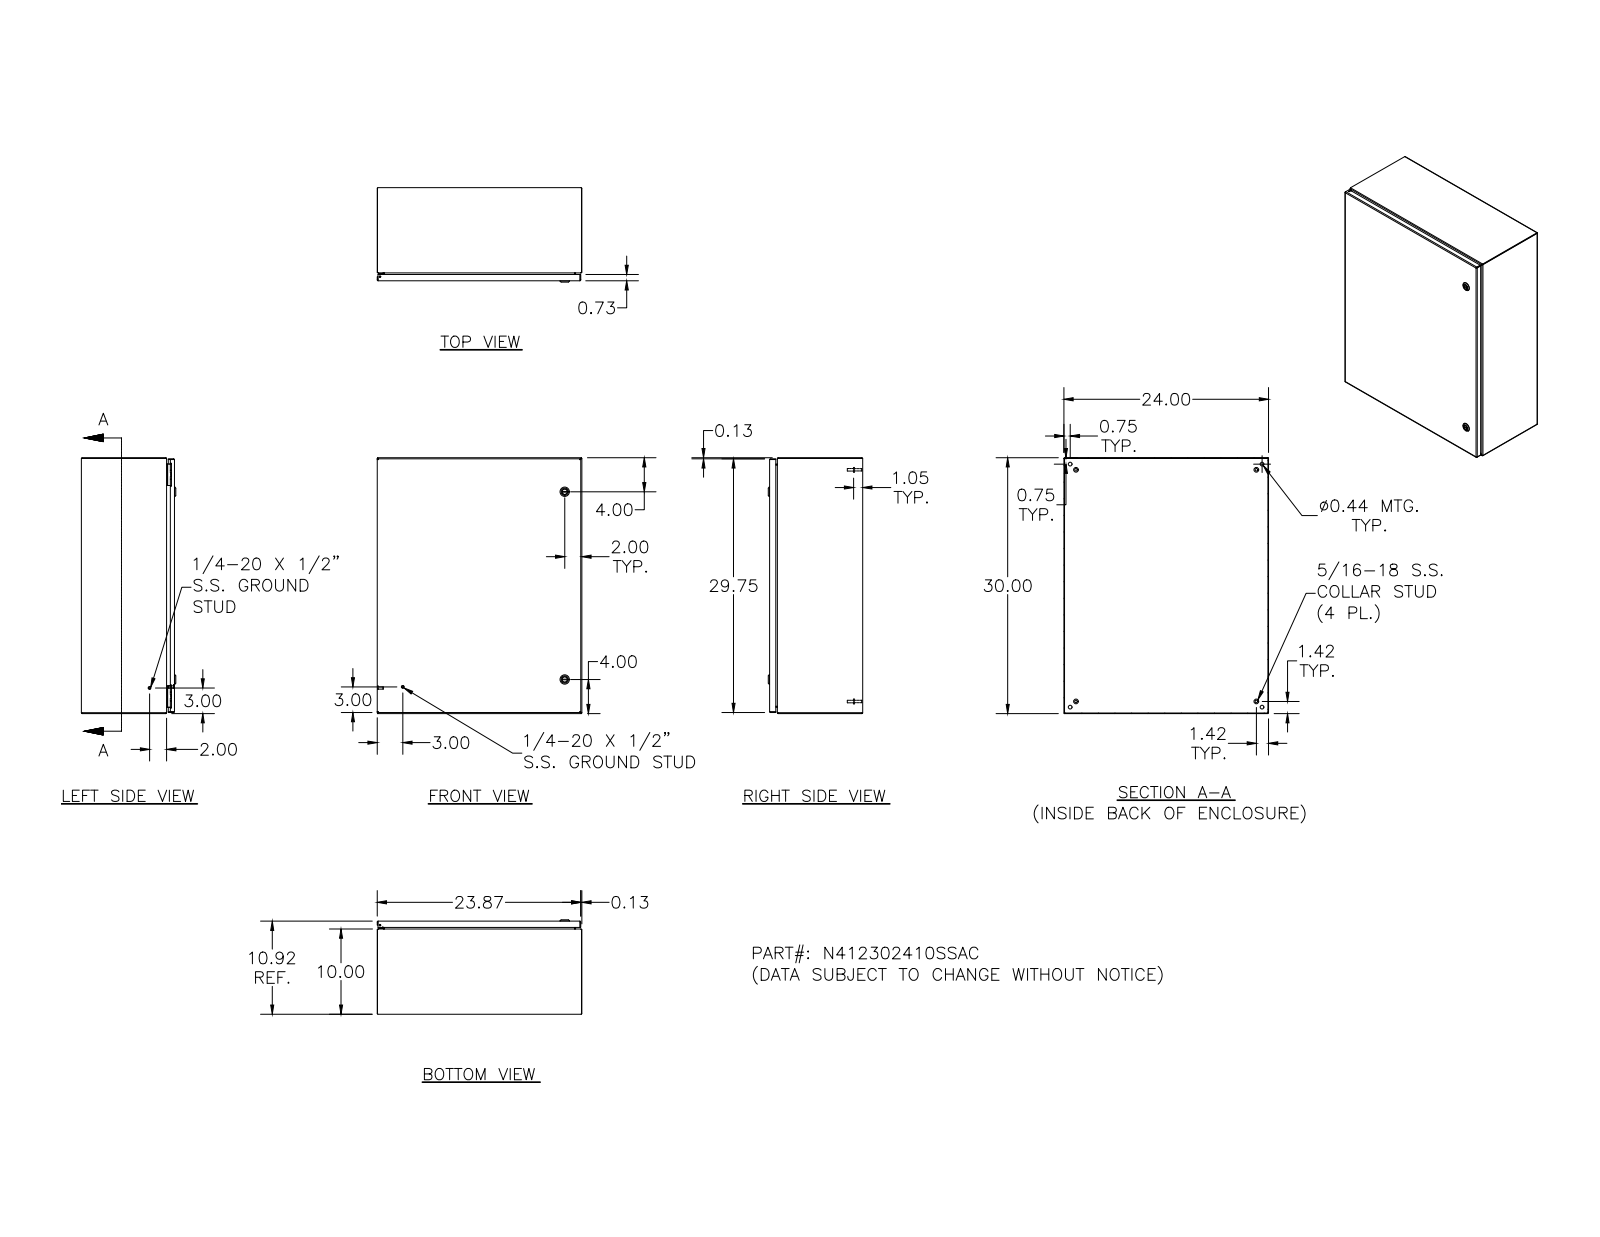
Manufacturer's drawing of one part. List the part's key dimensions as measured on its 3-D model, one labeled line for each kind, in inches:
Part name (STEP PRODUCT): N412302410SSAC; N412302410SSACBKP; 388151; N4123024SSACLID (+8 more)
STEP written by: Autodesk Inventor 2011 (AUTOMOTIVE_DESIGN)
Units: inches
Bodies: 42 solids, 1662 faces (698 planar, 588 cylindrical, 376 other)
Overall size (bounding box): 30 × 24 × 11.075
Volume: 203 in³ · Surface area: 5 506 in²
Round holes (diameter × count): ⌀0.188 ×5, ⌀0.093 ×4, ⌀0.152 ×4, ⌀0.167 ×4, ⌀0.172 ×4, ⌀0.437 ×4, ⌀0.156 ×2, ⌀0.197 ×2, ⌀0.315 ×2, ⌀0.394 ×2, ⌀0.402 ×2, ⌀0.634 ×2
Round bosses / shafts (diameter × count): ⌀0.25 ×10, ⌀0.563 ×4, ⌀0.36 ×4, ⌀0.32 ×4, ⌀0.3 ×4, ⌀0.275 ×4, ⌀0.256 ×4, ⌀0.164 ×4
Partial cylindrical surfaces — rounded edges, fillets, slot ends (radius × count): R0.05 ×26, R0.016 ×18, R0.016 ×16, R0.09 ×16, R0.02 ×15, R0.031 ×14, R0.125 ×14, R0.032 ×8
Main face-to-face distances: 0.074, 10.843, 10.917, 10.769, 23.926, 29.926, 23.852, 24, 30, 29.852
Hole centre spacings: 26, 0.017, 0.66, 22.869, 0.019, 0.5, 0.648, 0.652
